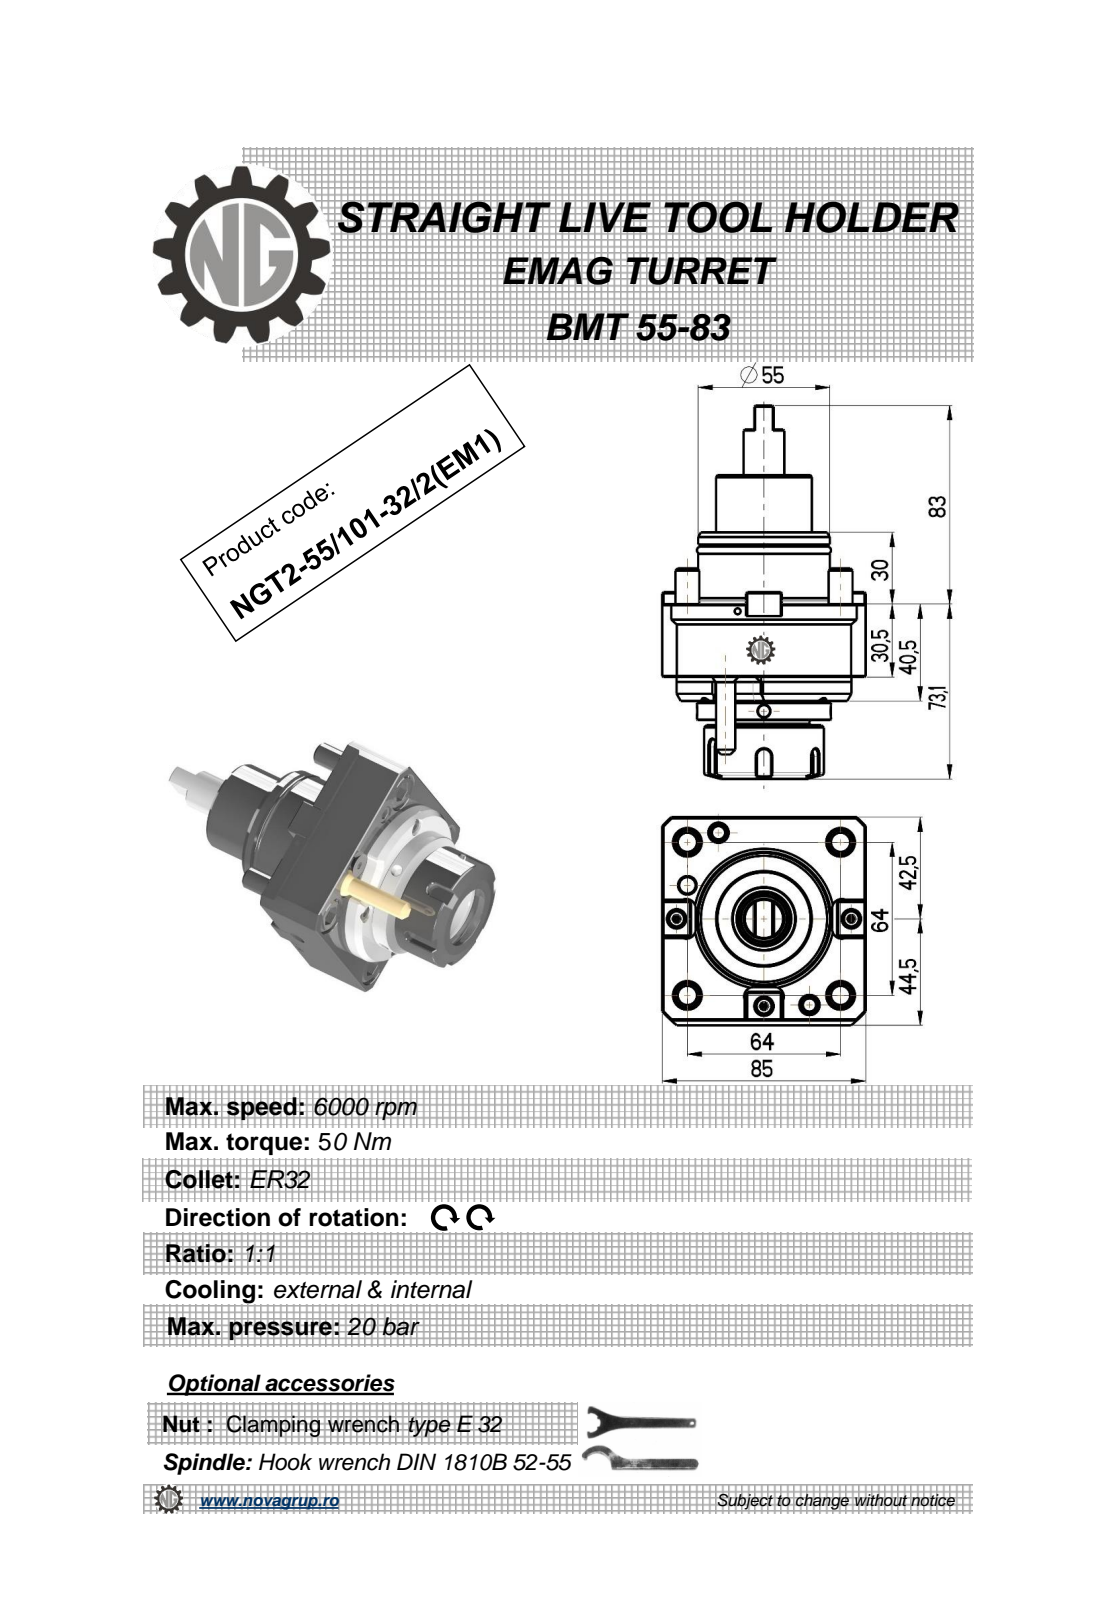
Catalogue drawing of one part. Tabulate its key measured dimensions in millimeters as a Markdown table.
| quantity | value |
| --- | --- |
| part name | NGT2_55_101_32_1_EM1 |
| STEP written by | PRO/ENGINEER BY PARAMETRIC TECHNOLOGY CORPORATION, 2010280 (CONFIG_CONTROL_DESIGN) |
| units | millimeters |
| bodies | 2 solids, 306 faces (140 planar, 69 cylindrical, 97 other) |
| overall size | 156.1 × 87 × 85 |
| volume | 438 439 mm³ |
| surface area | 52 080 mm² |
| round holes (diameter × count) | 5 × 3, 3 × 1, 6.8 × 1, 27 × 1 |
| round bosses / shafts (diameter × count) | 10 × 5, 73 × 1, 56 × 1, 55 × 1, 54.4 × 1, 50 × 1, 42 × 1, 40 × 1 |
| partial cylindrical surfaces (radius × count) | 0.2 × 6, 3 × 5, 0.8 × 2, 6 × 2, 57.5 × 1 |
| main face-to-face distances | 30.5, 85, 10, 40.5, 87, 18, 20.1, 8, 10.5, 48.5 |
| hole center spacings | 34.93, 37.12, 50.12 |
